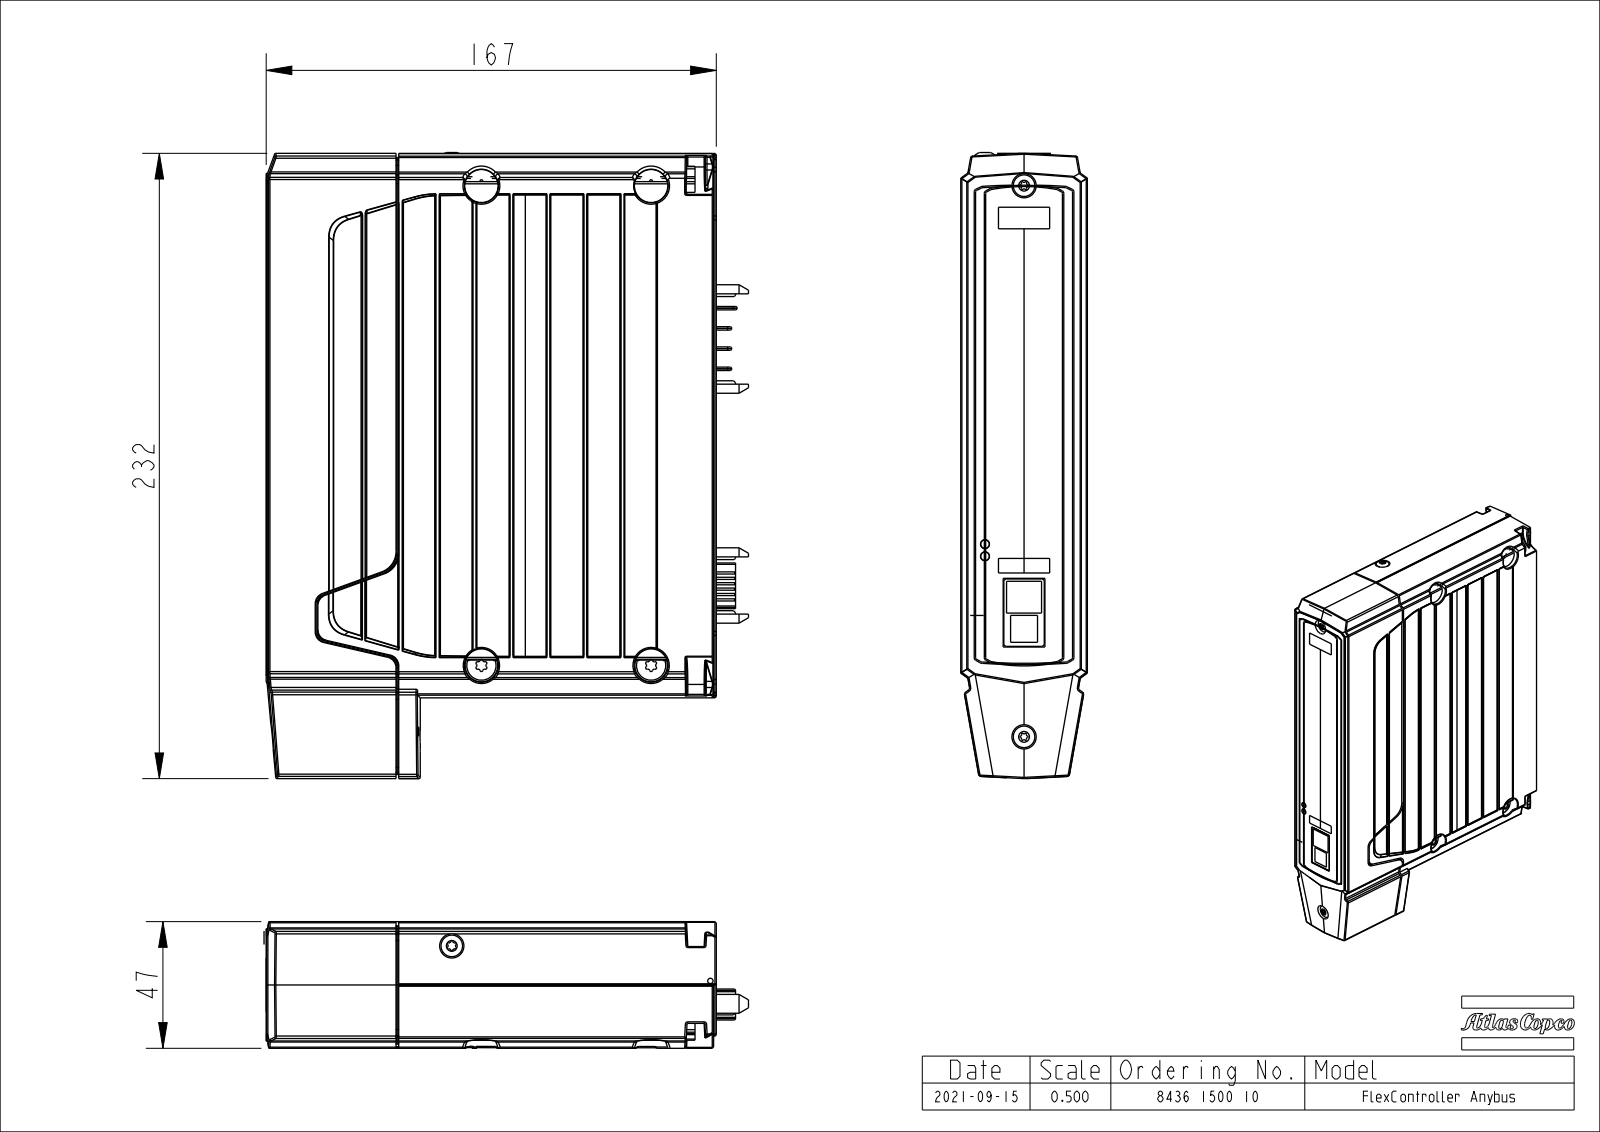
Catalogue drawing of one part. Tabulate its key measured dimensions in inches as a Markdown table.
| quantity | value |
| --- | --- |
| part name | 4222186912; FD_SIGNAL-PLUG_29; FD_POWER-PLUG_29; 4222184280_DESIGN_ASM (+8 more) |
| STEP written by | CREO PARAMETRIC BY PTC INC, 2020281 (CONFIG_CONTROL_DESIGN) |
| units | inches |
| bodies | 20 solids, 4926 faces (2358 planar, 1334 cylindrical, 1234 other) |
| overall size | 9.146 × 7.049 × 1.85 |
| volume | 81.77 in³ |
| surface area | 436.2 in² |
| round holes (diameter × count) | 0.098 × 8, 0.13 × 5, 0.165 × 3, 0.354 × 3, 0.102 × 2, 0.169 × 1, 0.335 × 1 |
| round bosses / shafts (diameter × count) | 0.315 × 6, 0.079 × 5, 0.374 × 4, 0.197 × 4, 0.157 × 4, 0.126 × 2, 0.098 × 2, 0.472 × 1 |
| partial cylindrical surfaces (radius × count) | 0.039 × 217, 0.012 × 167, 0.02 × 92, 0.004 × 85, 0.023 × 48, 0.004 × 32, 0.016 × 18, 0.024 × 18 |
| main face-to-face distances | 0.118, 0.846, 0.453, 0.394, 0.728, 0.335, 1.732, 1.614, 1.398, 1.004 |
| hole center spacings | 0.453, 1.299, 7.006, 7.126, 0.057, 0.177, 0.279, 0.463 |
